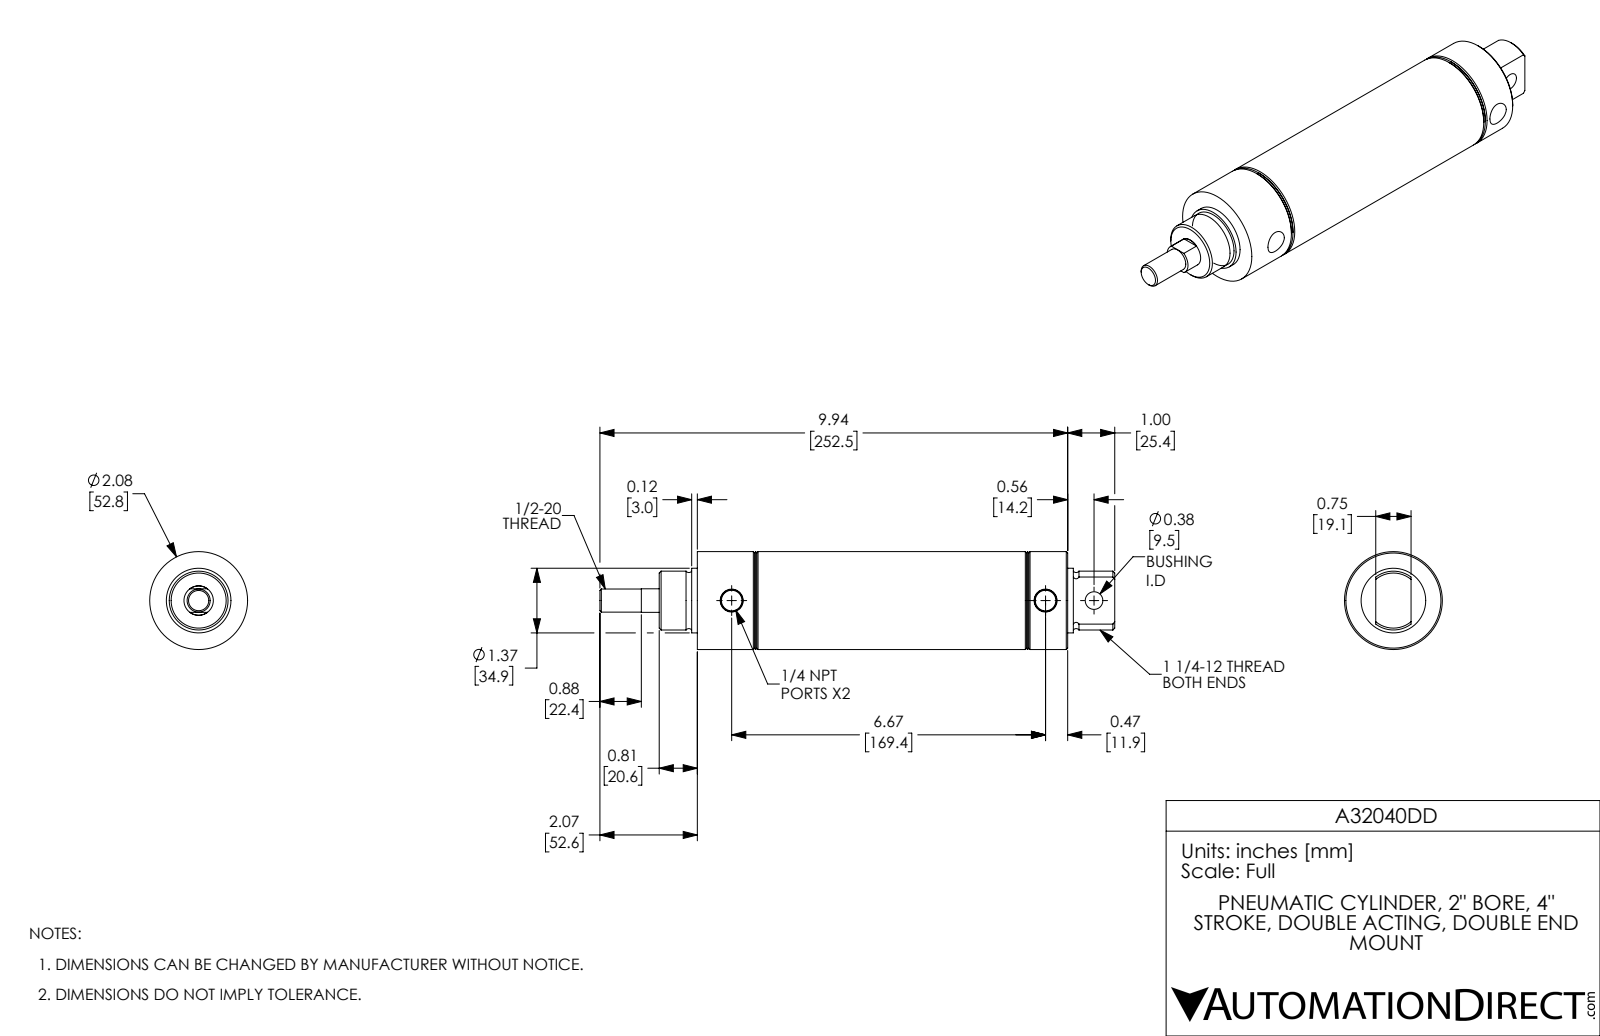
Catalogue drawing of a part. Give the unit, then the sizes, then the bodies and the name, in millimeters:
Units: millimetres
Overall size (bounding box): 277.9 × 52.8 × 52.8
Round holes (diameter × count): ⌀11.1 ×2, ⌀9.5 ×1, ⌀15.9 ×1, ⌀50.8 ×1
Round bosses / shafts (diameter × count): ⌀52.8 ×1, ⌀34.9 ×1, ⌀31.8 ×1, ⌀12.5 ×1
Main face-to-face distances: 12.7, 114.3, 101.6, 157.1, 144.4, 42.8, 42.8, 55.5, 157.1, 199.9
Hole centre spacings: 26.2, 169.4, 195.6
Volume: 282 300 mm³ · Surface area: 84 770 mm²
Bodies: 2 solids, 88 faces (20 planar, 30 cylindrical, 38 other)
Part name (STEP PRODUCT): A32040DD-MainBody; A32040DD-Rod; A32040DD
STEP written by: SolidWorks 2017 (AUTOMOTIVE_DESIGN)
